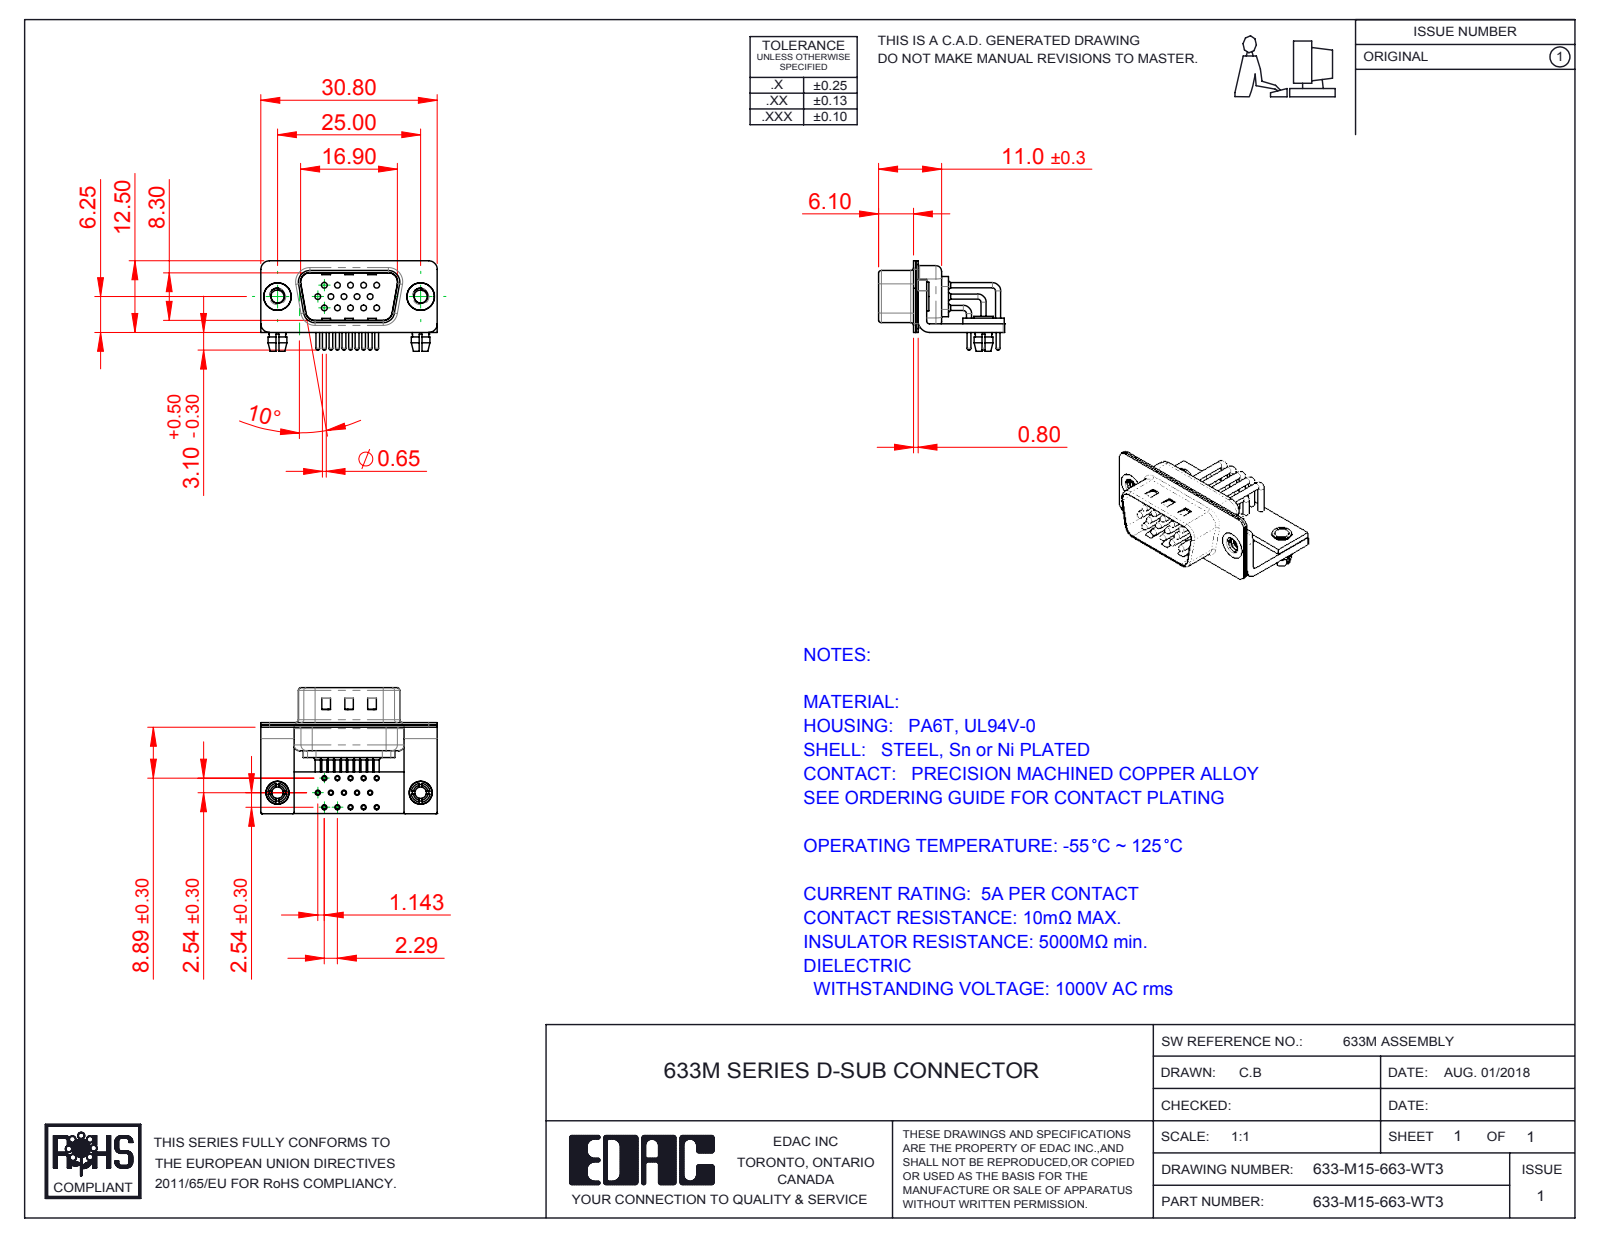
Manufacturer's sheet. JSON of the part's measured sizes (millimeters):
{"part_name": "633M Contact Row 3; 633M Stabilizer Board_15 Contacts; 633M Contact Row 1; 633M Board Lock (+7 more)", "step_written_by": "SolidWorks 2016 (CONFIG_CONTROL_DESIGN)", "units": "millimeters", "bodies": {"solids": 25, "faces": 2126, "planar": 1141, "cylindrical": 753, "other": 232}, "overall_size": [30.8, 22, 15.8], "volume_mm3": 1972, "surface_area_mm2": 6011, "round_holes": [[2, 17], [0.9, 15], [1, 15], [1.7, 15], [2.26, 2], [2.5, 2], [3.2, 2], [4, 2], [4.8, 2]], "round_bosses_or_shafts": [[0.9, 16], [1.5, 15], [0.65, 15], [5, 2], [4.9, 2], [4, 2], [3.4, 2], [3.3, 2]], "partial_cylinders_radius": [[0.25, 16], [1.5, 16], [1.01, 15], [2, 13], [0.5, 9], [1.6, 8], [0.6, 4], [0.65, 4]], "face_to_face_distances": [0.4, 1.5, 0.8, 1, 0.85, 1.9, 2.5, 1.25, 10.4, 9.55], "hole_center_spacings": [2.29, 4.57, 2.28, 3.96, 2.78, 4.27, 6.05, 6.86]}
